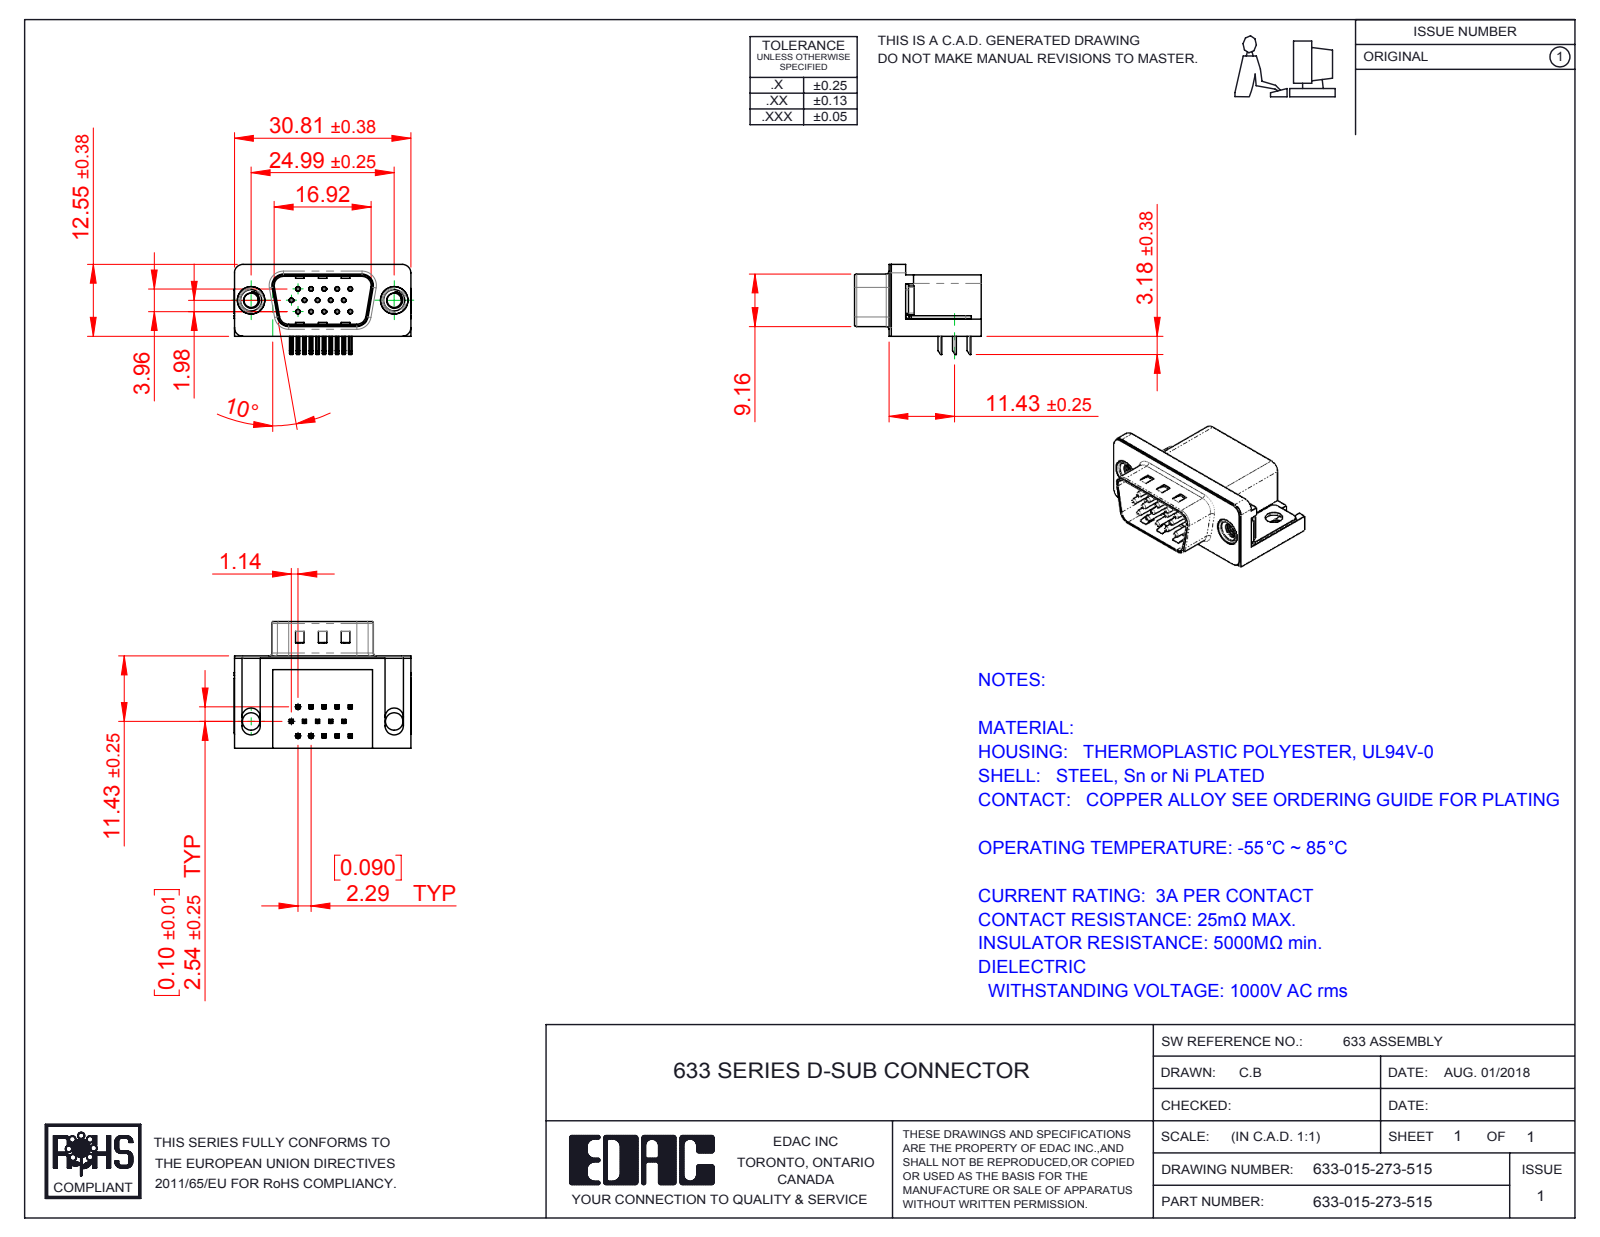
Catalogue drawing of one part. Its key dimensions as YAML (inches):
part_name: "633 Thru Hole Board Mount; 633 Contact Middle_Recessed; 633-015-273-515; 633 Contact Middle (+5 more)"
step_written_by: "SolidWorks 2016 (CONFIG_CONTROL_DESIGN)"
units: inches
bodies: {solids: 21, faces: 1441, planar: 859, cylindrical: 447, other: 135}
overall_size: [1.216, 0.87, 0.619]
volume: 0.248
surface_area: 8.389
round_holes:
  - {diameter: 0.014, count: 15}
  - {diameter: 0.031, count: 15}
  - {diameter: 0.098, count: 2}
  - {diameter: 0.12, count: 2}
  - {diameter: 0.157, count: 2}
  - {diameter: 0.189, count: 2}
  - {diameter: 0.197, count: 2}
round_bosses_or_shafts:
  - {diameter: 0.03, count: 15}
  - {diameter: 0.193, count: 2}
  - {diameter: 0.187, count: 2}
  - {diameter: 0.154, count: 2}
partial_cylinders:
  - {radius: 0.01, count: 68}
  - {radius: 0.005, count: 30}
  - {radius: 0.039, count: 16}
  - {radius: 0.02, count: 9}
  - {radius: 0.063, count: 8}
  - {radius: 0.059, count: 7}
  - {radius: 0.035, count: 4}
  - {radius: 0.079, count: 4}
face_to_face_distances: [0.016, 0.407, 0.618, 0.114, 0.02, 0.264, 0.634, 0.098, 0.014, 0.421]
hole_center_spacings: [0.156, 0.09, 0.18, 0.09, 0.238, 0.27, 0.312, 0.238]
